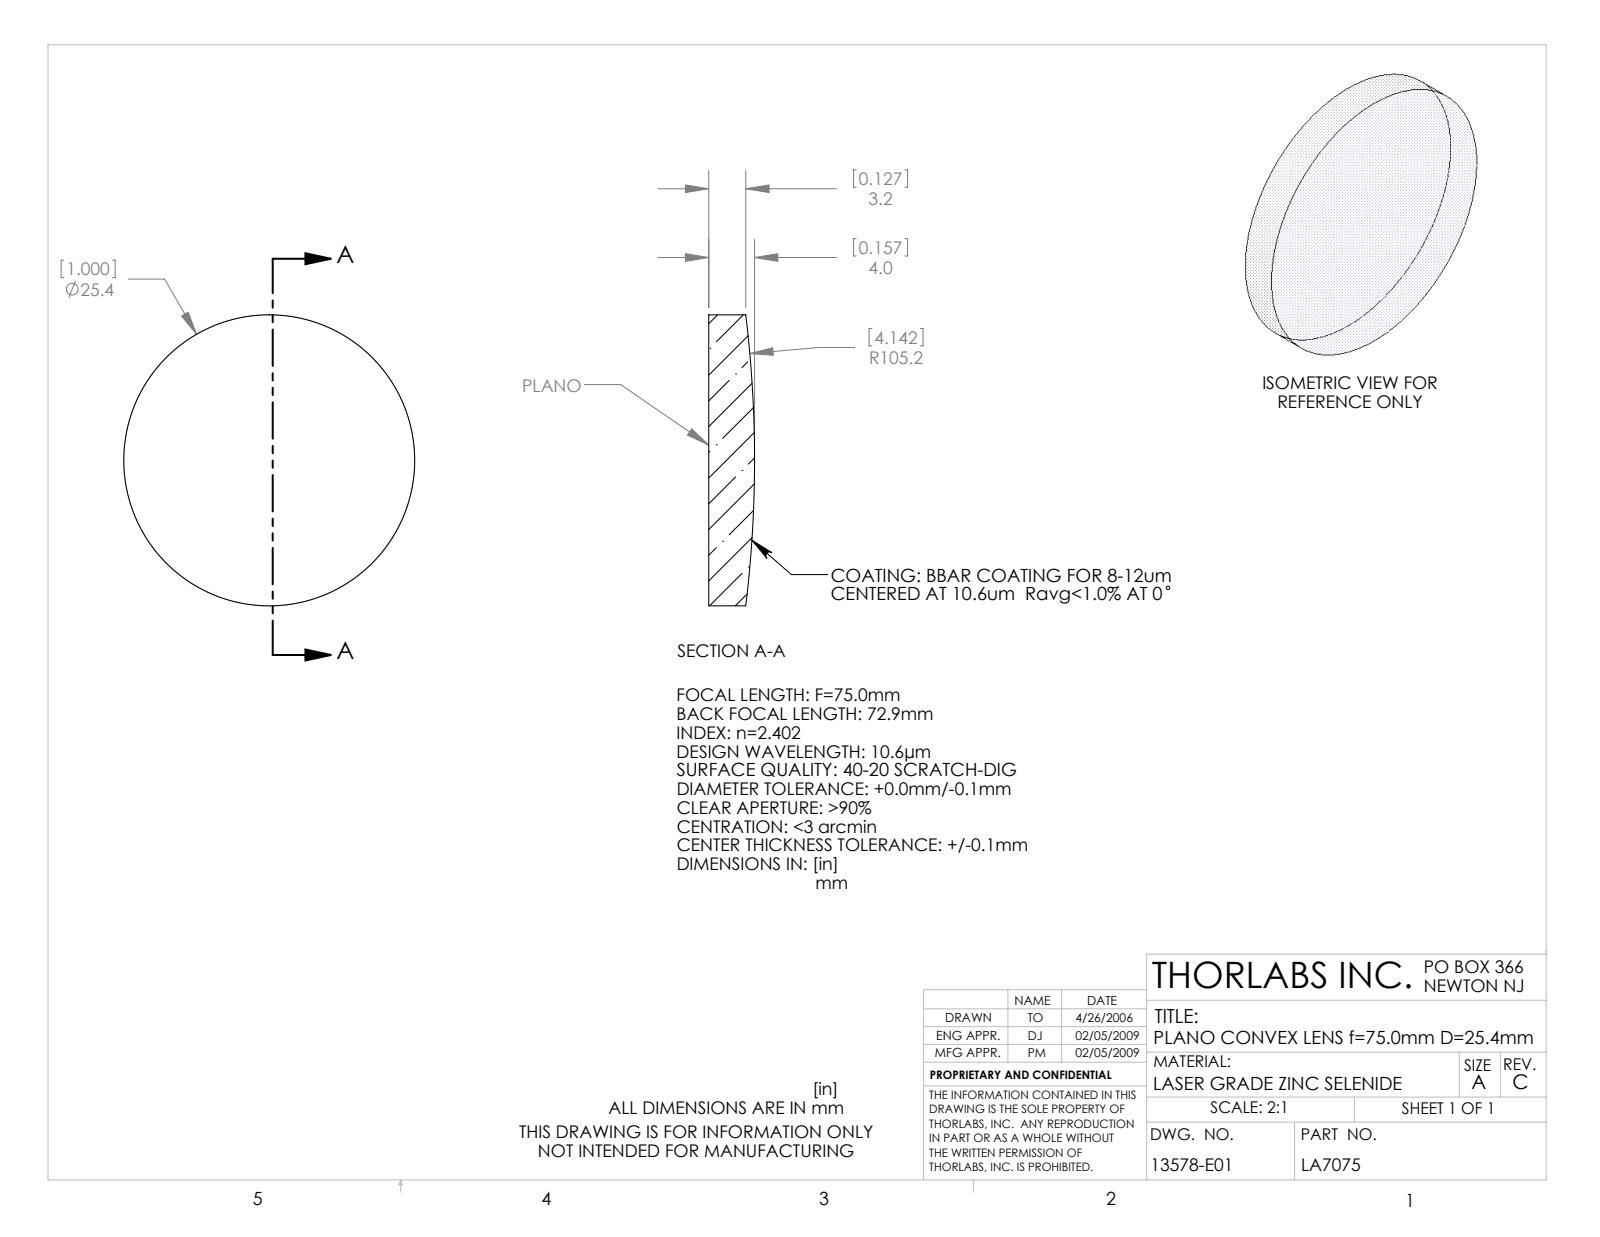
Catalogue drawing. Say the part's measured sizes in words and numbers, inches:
The part is named "13578-E0W". Its 3-D file was written by "SolidWorks 2007 (AUTOMOTIVE_DESIGN)". It is 0 solids with 5 faces: 1 planar, 2 cylindrical and 2 other. Overall it measures 1 by 1 by 0.157 inches. Round bosses or shafts: 1 of diameter 1.
